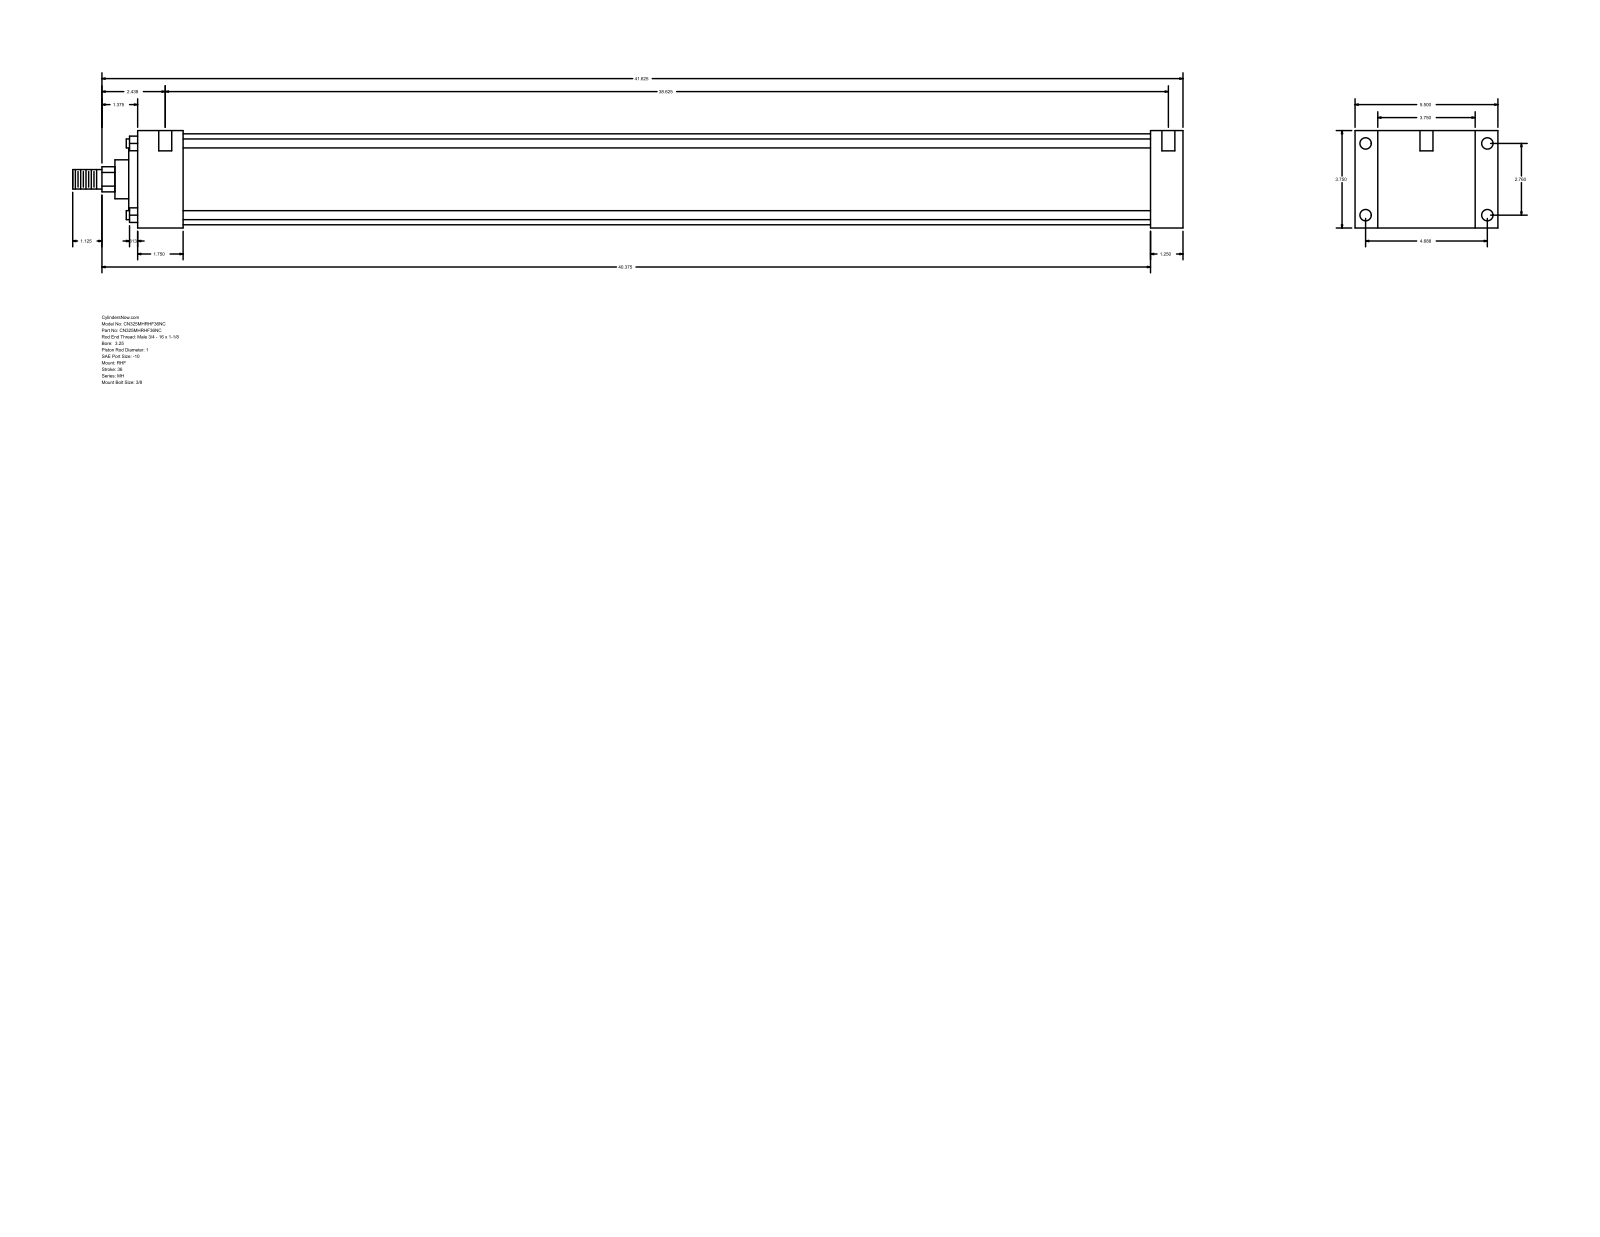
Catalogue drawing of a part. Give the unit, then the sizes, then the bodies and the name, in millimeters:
Units: millimetres
Overall size (bounding box): 1085.85 × 139.7 × 95.25
Round holes (diameter × count): ⌀5.56 ×4, ⌀11.13 ×4, ⌀12.7 ×2
Round bosses / shafts (diameter × count): ⌀8.76 ×4, ⌀88.9 ×1, ⌀60.33 ×1, ⌀38.1 ×1, ⌀25.4 ×1, ⌀19.05 ×1
Partial cylindrical surfaces — rounded edges, fillets, slot ends (radius × count): R12.29 ×1
Main face-to-face distances: 95.24, 31.75, 22.23, 117.47, 990.61, 1022.36, 139.7, 44.46, 946.15, 977.9
Hole centre spacings: 70.1, 119.06, 138.16, 987.42, 1.58, 4.76, 981.08, 982.66
Bodies: 0 solids, 90 faces (61 planar, 29 cylindrical, 0 other)
Part name (STEP PRODUCT): MH_RHF__0325_1
STEP written by: GSSL Pune (CONFIG_CONTROL_DESIGN)
